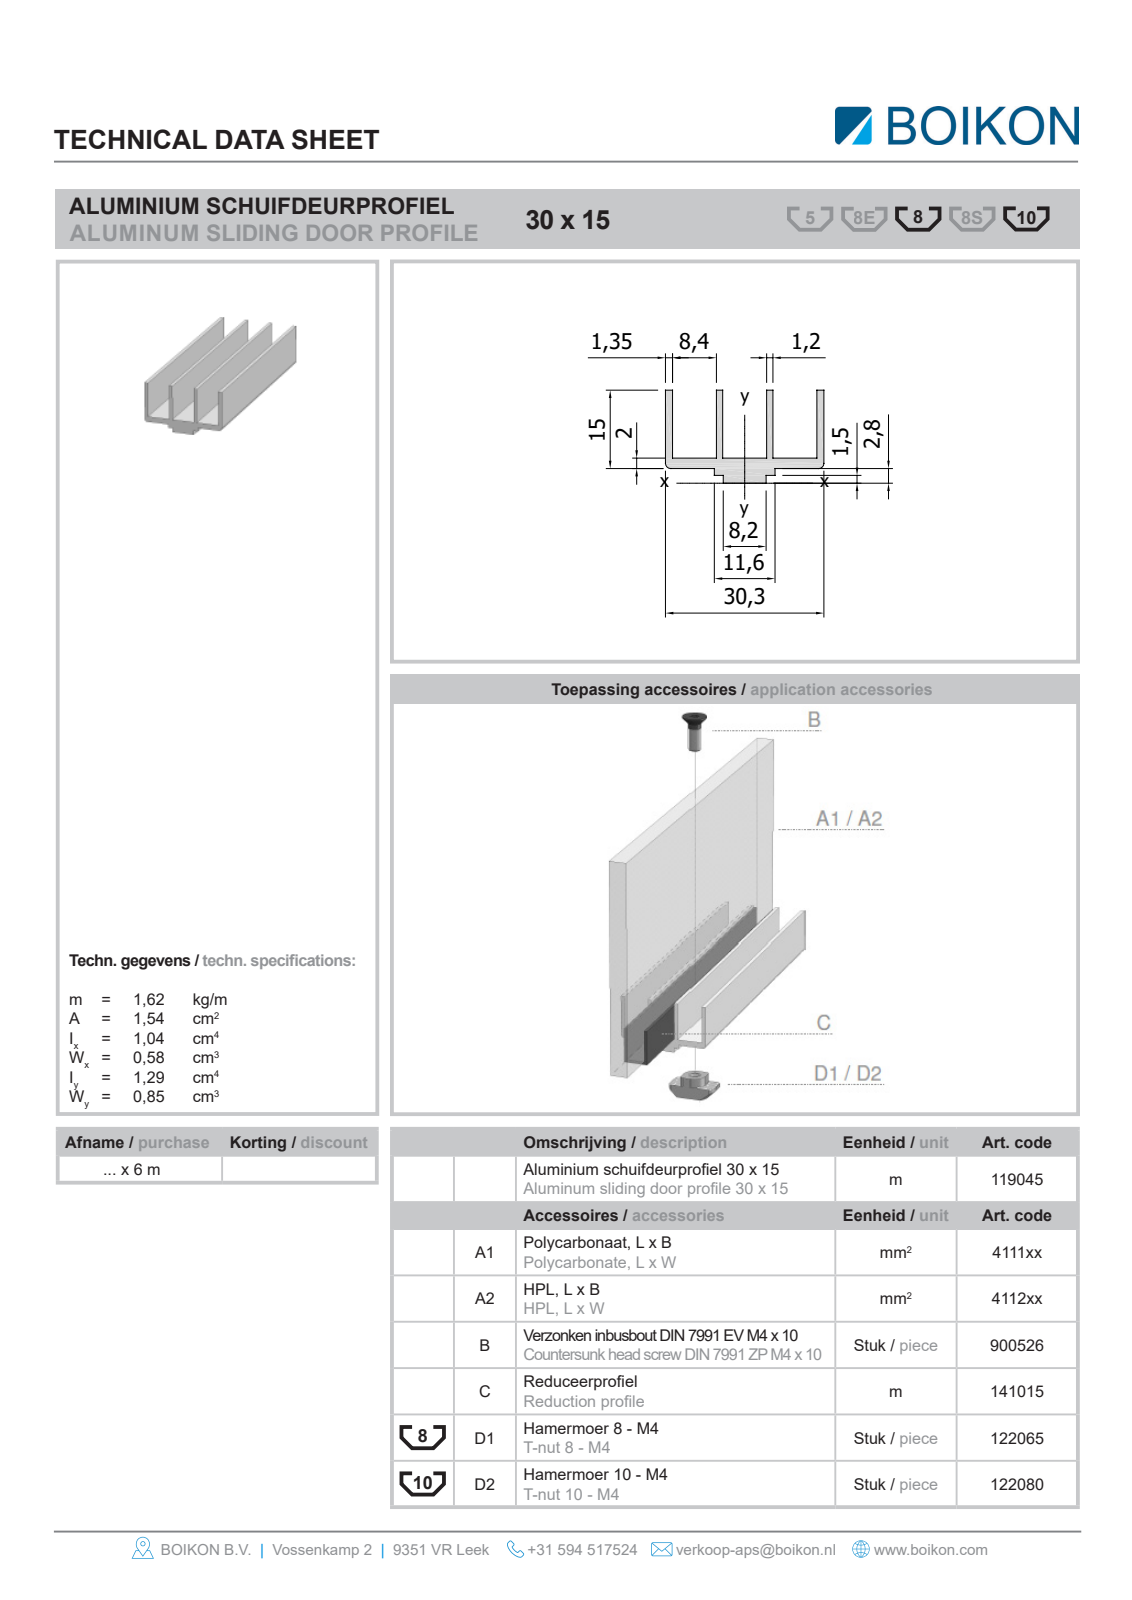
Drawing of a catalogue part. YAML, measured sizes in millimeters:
part_name: "Root; 119045Alu Schuifdeurprofiel 30x15BOIKON0"
step_written_by: "HiCAD 2013 1802.4 Build 509 (AUTOMOTIVE_DESIGN)"
units: millimeters
bodies: {solids: 1, faces: 28, planar: 26, cylindrical: 2, other: 0}
overall_size: [1000, 30.3, 17.8]
volume: 153851
surface_area: 173649
partial_cylinders:
  - {radius: 1, count: 2}
face_to_face_distances: [9.6, 8.4, 1.35, 9.75, 10.95, 19.35, 20.55, 28.95, 18, 19.2]
